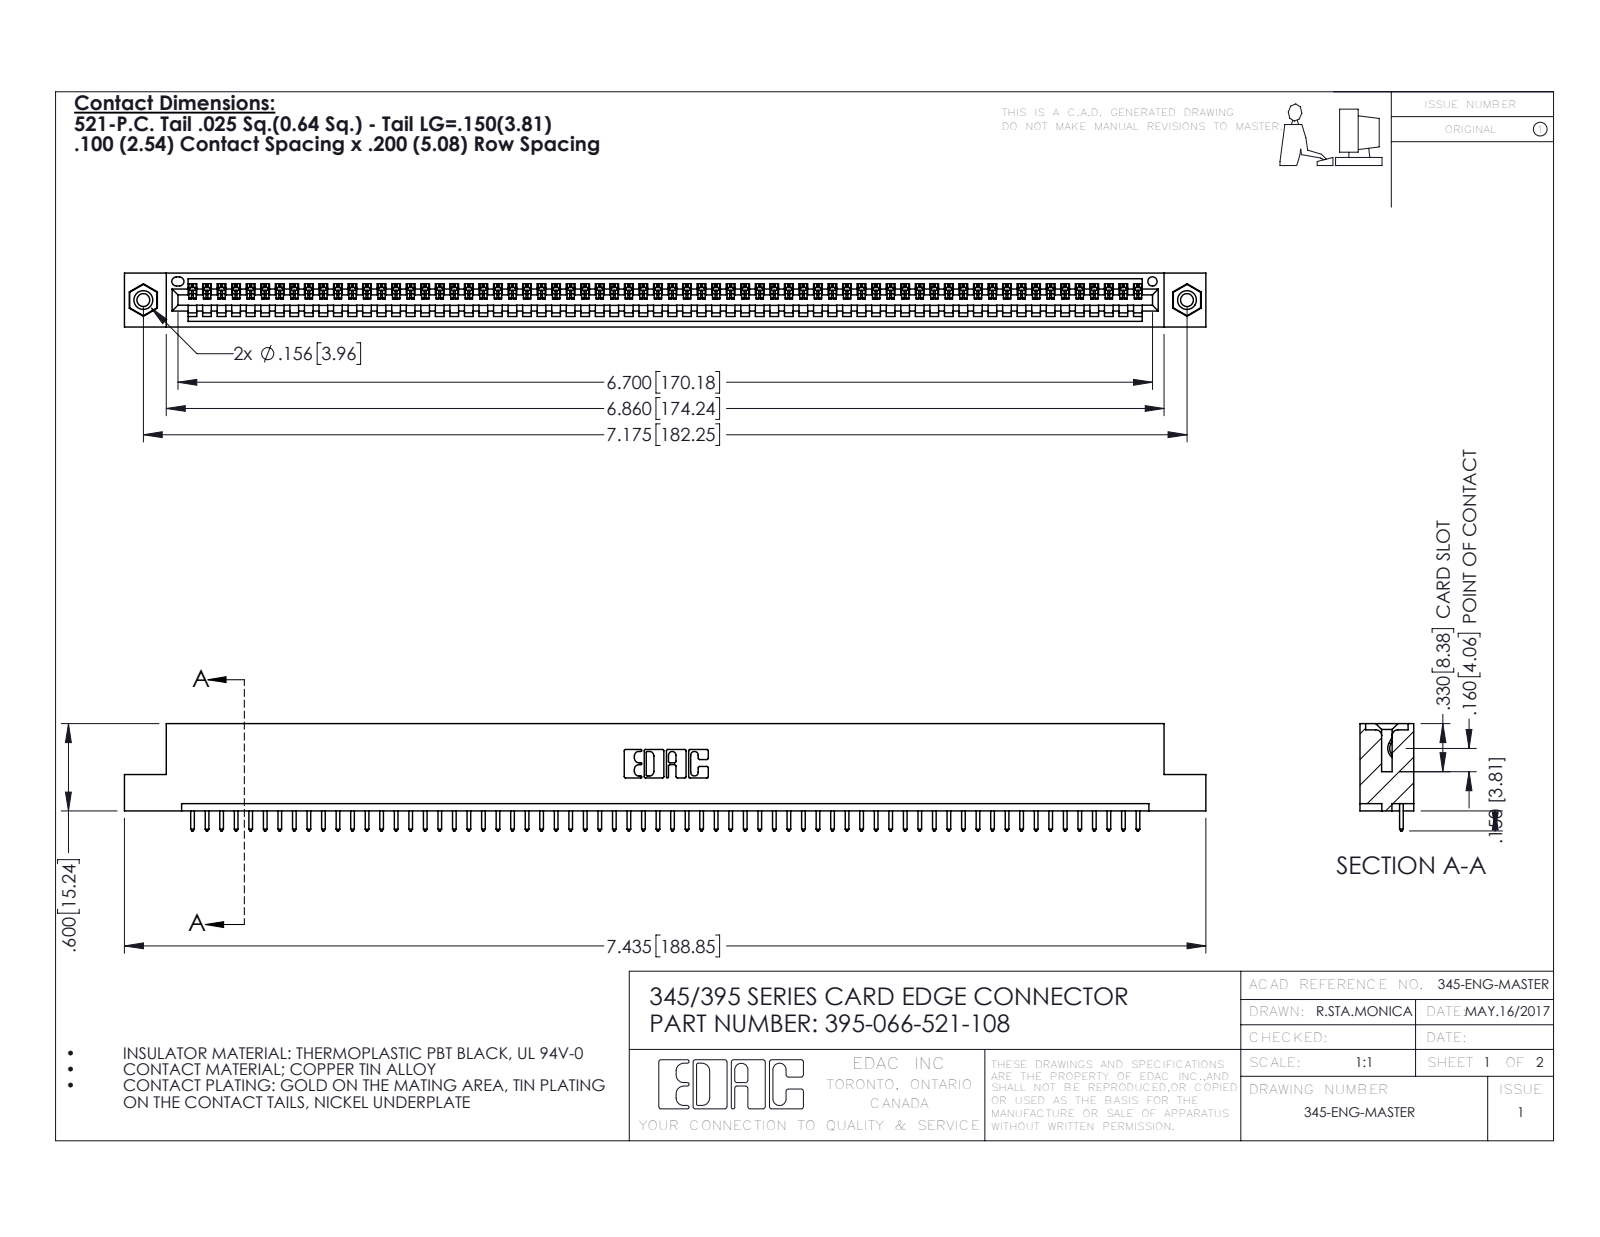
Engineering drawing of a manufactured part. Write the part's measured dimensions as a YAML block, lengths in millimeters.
part_name: "345-250-001_345-250-003-102; 345-292-001_345-293-121; 395-066-521-108; 345 Part_Flush Mounting Lugs - 0.156 Dia-TI"
step_written_by: "SolidWorks 2016 (CONFIG_CONTROL_DESIGN)"
units: millimeters
bodies: {solids: 69, faces: 4014, planar: 2752, cylindrical: 1246, other: 16}
overall_size: [188.8, 18.7, 9.4]
volume: 17940
surface_area: 23450
round_holes:
  - {diameter: 2.3, count: 2}
  - {diameter: 3.2, count: 2}
  - {diameter: 4, count: 2}
  - {diameter: 1.6, count: 1}
round_bosses_or_shafts:
  - {diameter: 3.9, count: 2}
partial_cylinders:
  - {radius: 0.2, count: 132}
  - {radius: 0.3, count: 132}
  - {radius: 0.3, count: 22}
  - {radius: 0.2, count: 6}
  - {radius: 0.8, count: 6}
  - {radius: 0.7, count: 3}
  - {radius: 0.8, count: 2}
  - {radius: 1, count: 2}
face_to_face_distances: [1.8, 7.6, 9.4, 5.1, 2.5, 6.9, 0.6, 5.7, 3.8, 1.8]
hole_center_spacings: [6.9, 176.3, 182.2]
